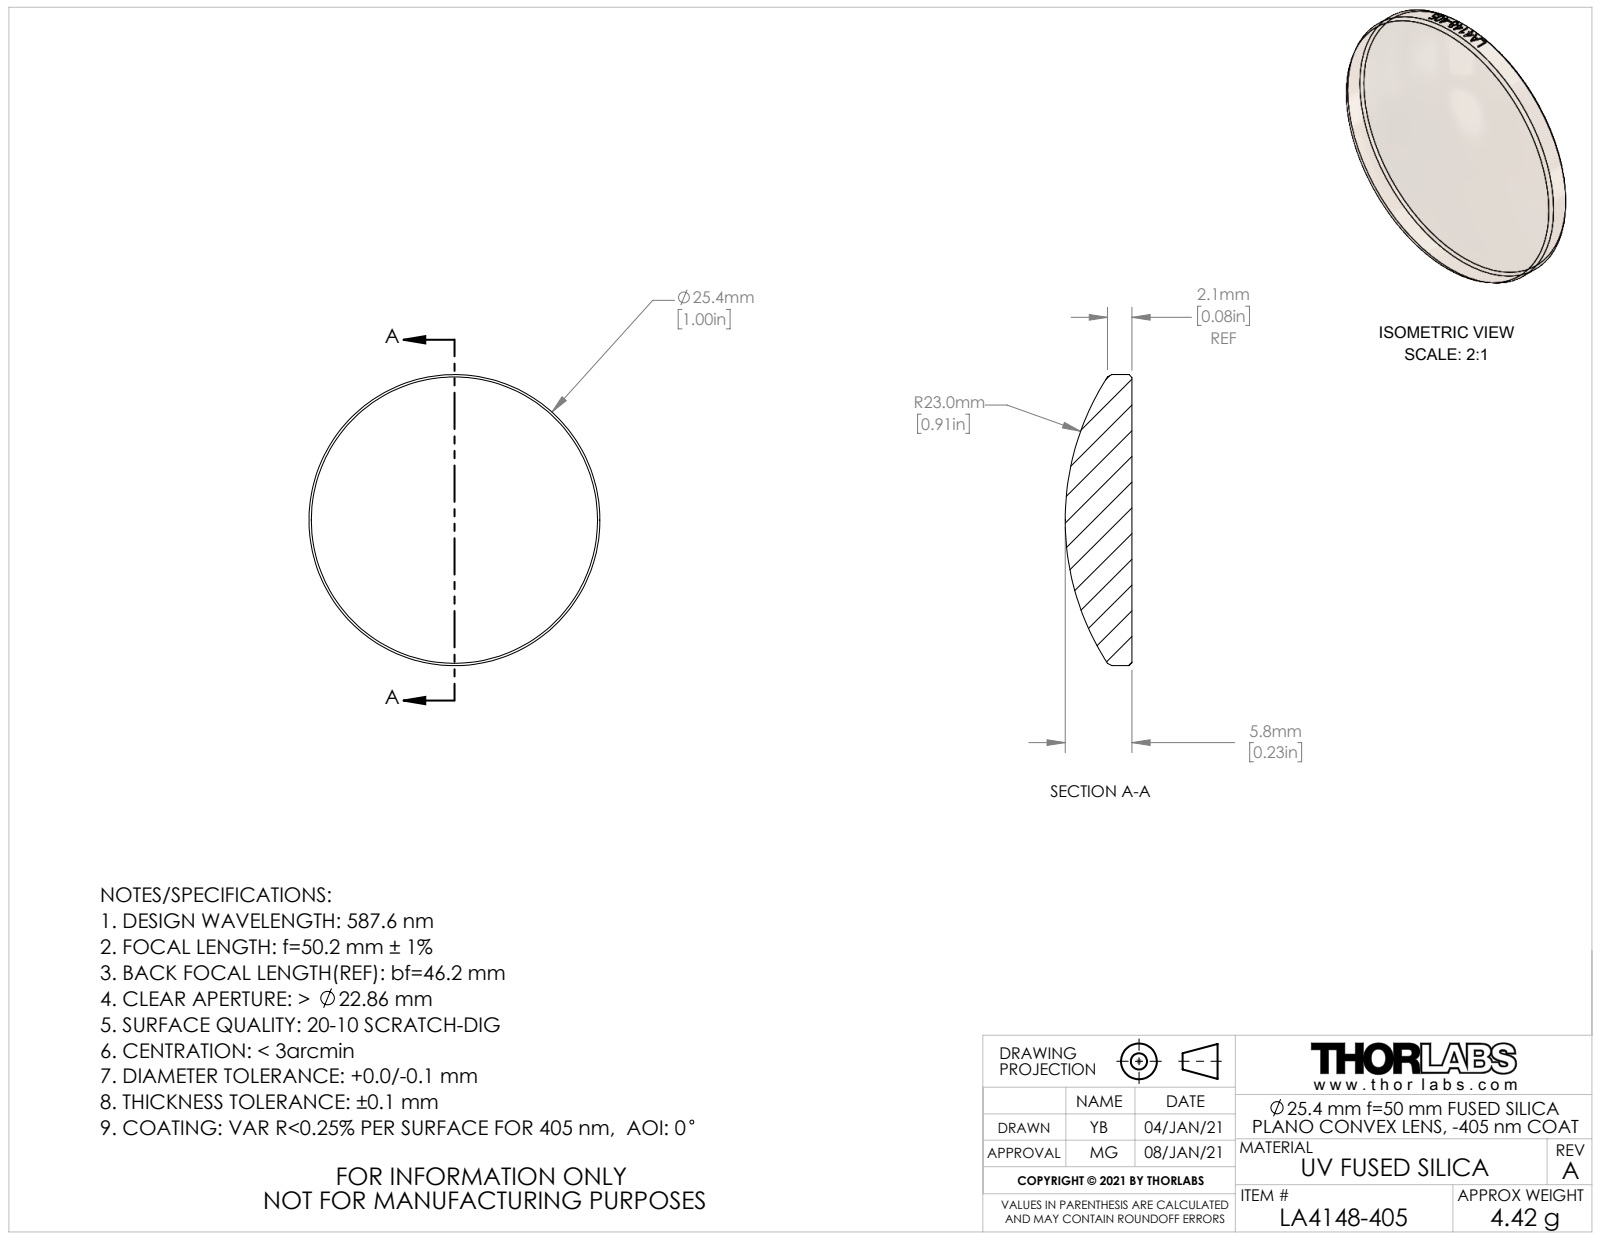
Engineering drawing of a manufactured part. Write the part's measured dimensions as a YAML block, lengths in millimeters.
part_name: "CTN016845; CTN016825-E0W"
step_written_by: "SolidWorks 2018 (AUTOMOTIVE_DESIGN)"
units: millimeters
bodies: {solids: 1, faces: 26, planar: 1, cylindrical: 19, other: 6}
overall_size: [25.4, 25.4, 5.8]
volume: 2000
surface_area: 1202
round_bosses_or_shafts:
  - {diameter: 25.4, count: 1}
